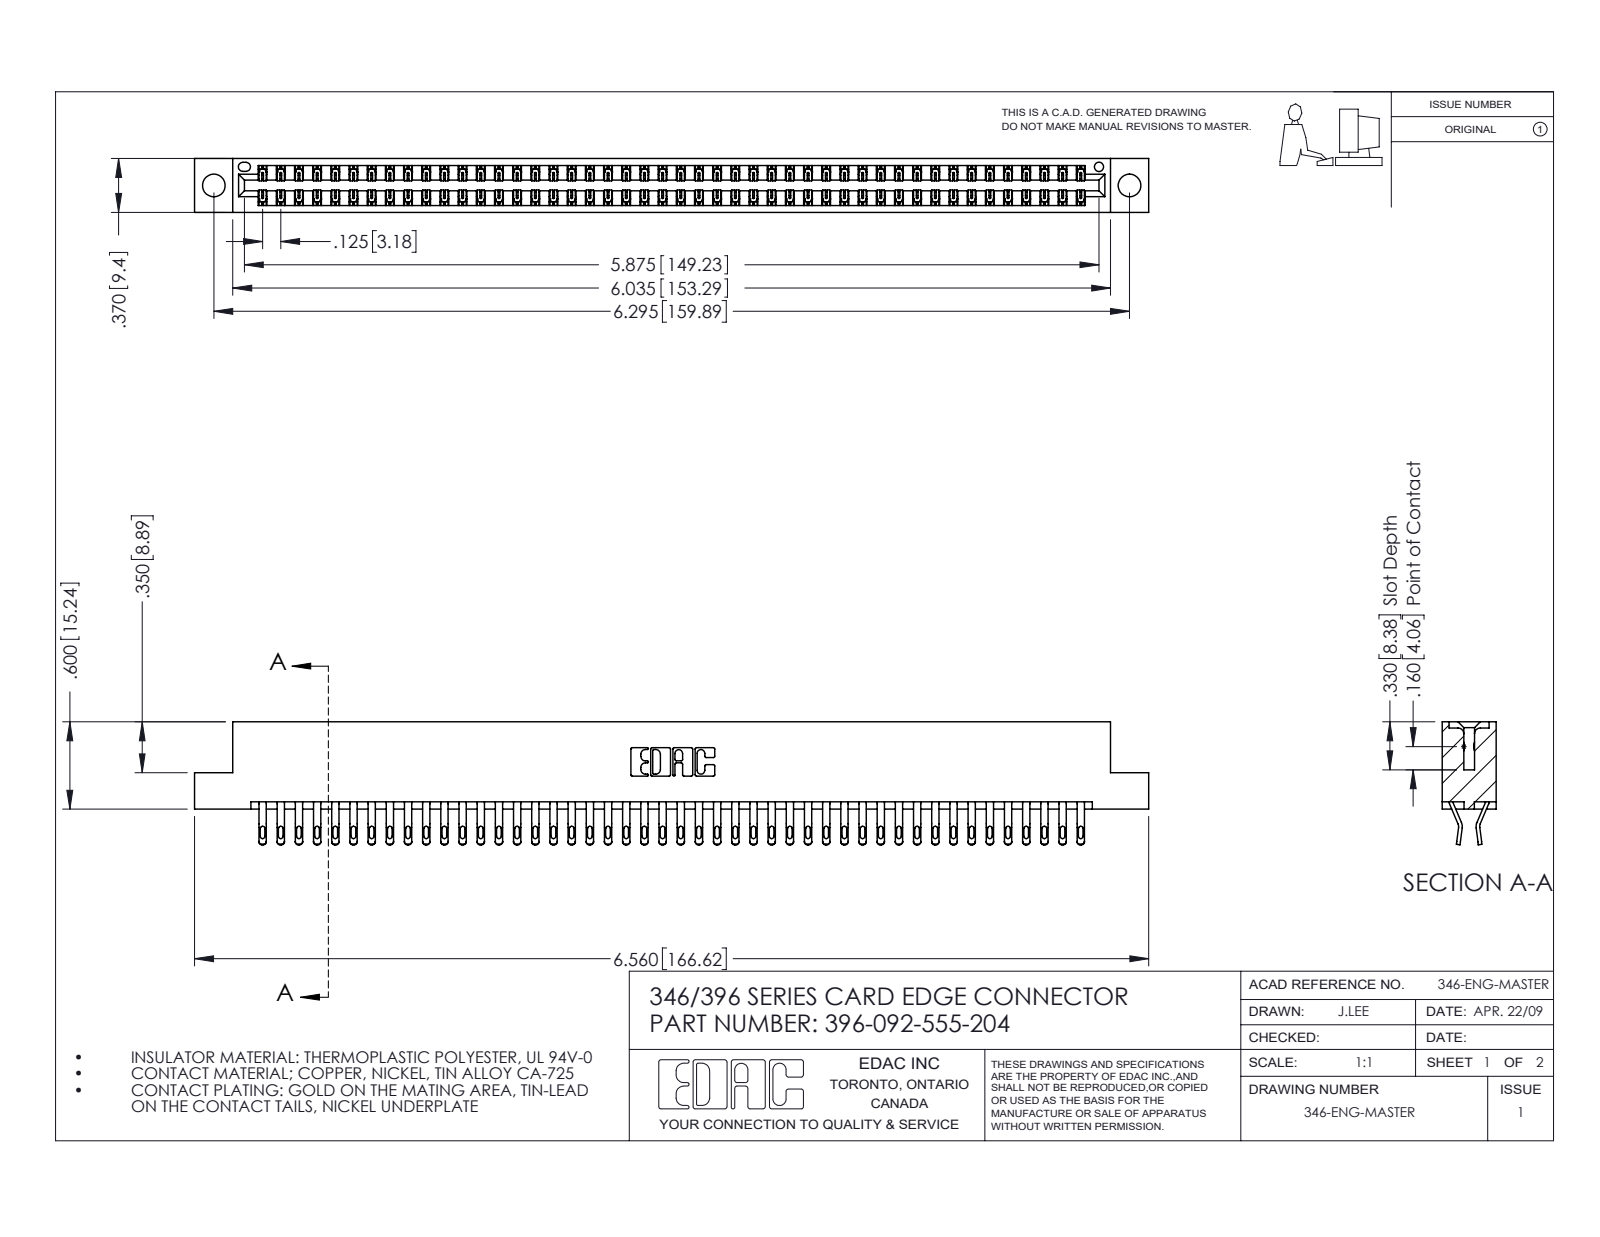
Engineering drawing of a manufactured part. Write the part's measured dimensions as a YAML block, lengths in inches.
part_name: "345-292-001_555 Tail; 346 Part_Flush Mounting Lugs - 0.156 Dia-TH; 396-092-555-204"
step_written_by: "SolidWorks 2016 (CONFIG_CONTROL_DESIGN)"
units: inches
bodies: {solids: 93, faces: 5458, planar: 3112, cylindrical: 2346, other: 0}
overall_size: [6.56, 0.845, 0.37]
volume: 1.004
surface_area: 36.35
round_holes:
  - {diameter: 0.156, count: 2}
  - {diameter: 0.064, count: 1}
partial_cylinders:
  - {radius: 0.016, count: 184}
  - {radius: 0.02, count: 184}
  - {radius: 0.006, count: 138}
  - {radius: 0.01, count: 22}
  - {radius: 0.007, count: 6}
  - {radius: 0.031, count: 6}
  - {radius: 0.026, count: 3}
  - {radius: 0.01, count: 2}
face_to_face_distances: [0.048, 0.322, 0.37, 0.25, 0.025, 0.072, 0.298, 0.275, 0.148, 0.222]
hole_center_spacings: [0.246, 6.086, 6.295]
